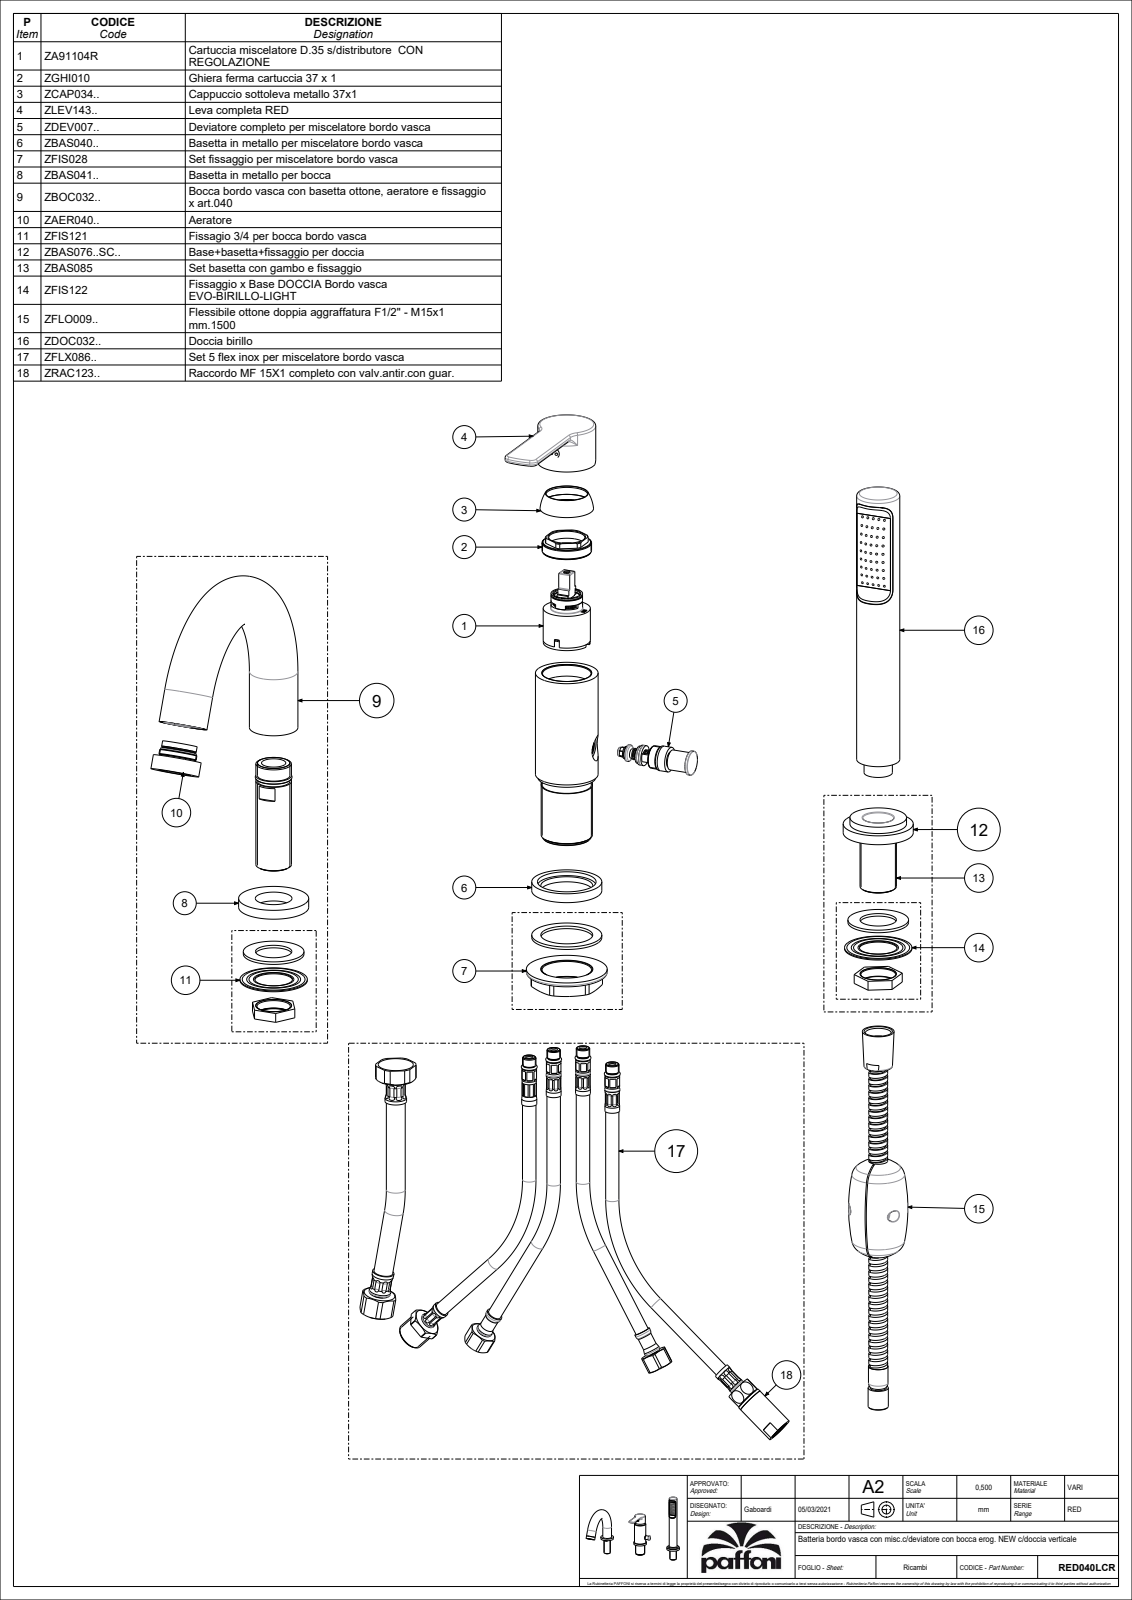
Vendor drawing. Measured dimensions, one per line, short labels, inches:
name: RED040LCR
written by: CREO PARAMETRIC BY PTC INC, 2020044 (CONFIG_CONTROL_DESIGN)
unit: in
bodies: 4 solids, 2230 faces (1235 planar, 678 cylindrical, 317 other)
size: 13.858 × 8.78 × 8.103
volume: 18.58 in³; area: 307.3 in²
holes: 61× ⌀0.02, 45× ⌀0.059, 6× ⌀0.276, 3× ⌀1.937, 2× ⌀0.13, 2× ⌀0.157, 2× ⌀0.177, 2× ⌀0.748, 2× ⌀1.055, 2× ⌀1.071, 2× ⌀1.299, 2× ⌀1.339
bosses: 3× ⌀2.047, 3× ⌀1.74, 2× ⌀1.417, 2× ⌀1.335, 1× ⌀1.831, 1× ⌀1.693, 1× ⌀1.654, 1× ⌀1.496
rounds: 66× R0.02, 30× R0.01, 11× R0.006, 4× R0.012, 4× R0.059, 4× R0.394, 2× R0.039, 2× R0.197
face distances: 0.276, 4.689, 0.079, 0.197, 4.413, 0.177, 0.472, 0.394, 4.866, 4.591
hole spacings: 0.15, 0.311, 0.226, 0.075, 0.542, 0.788, 0.256, 0.512
